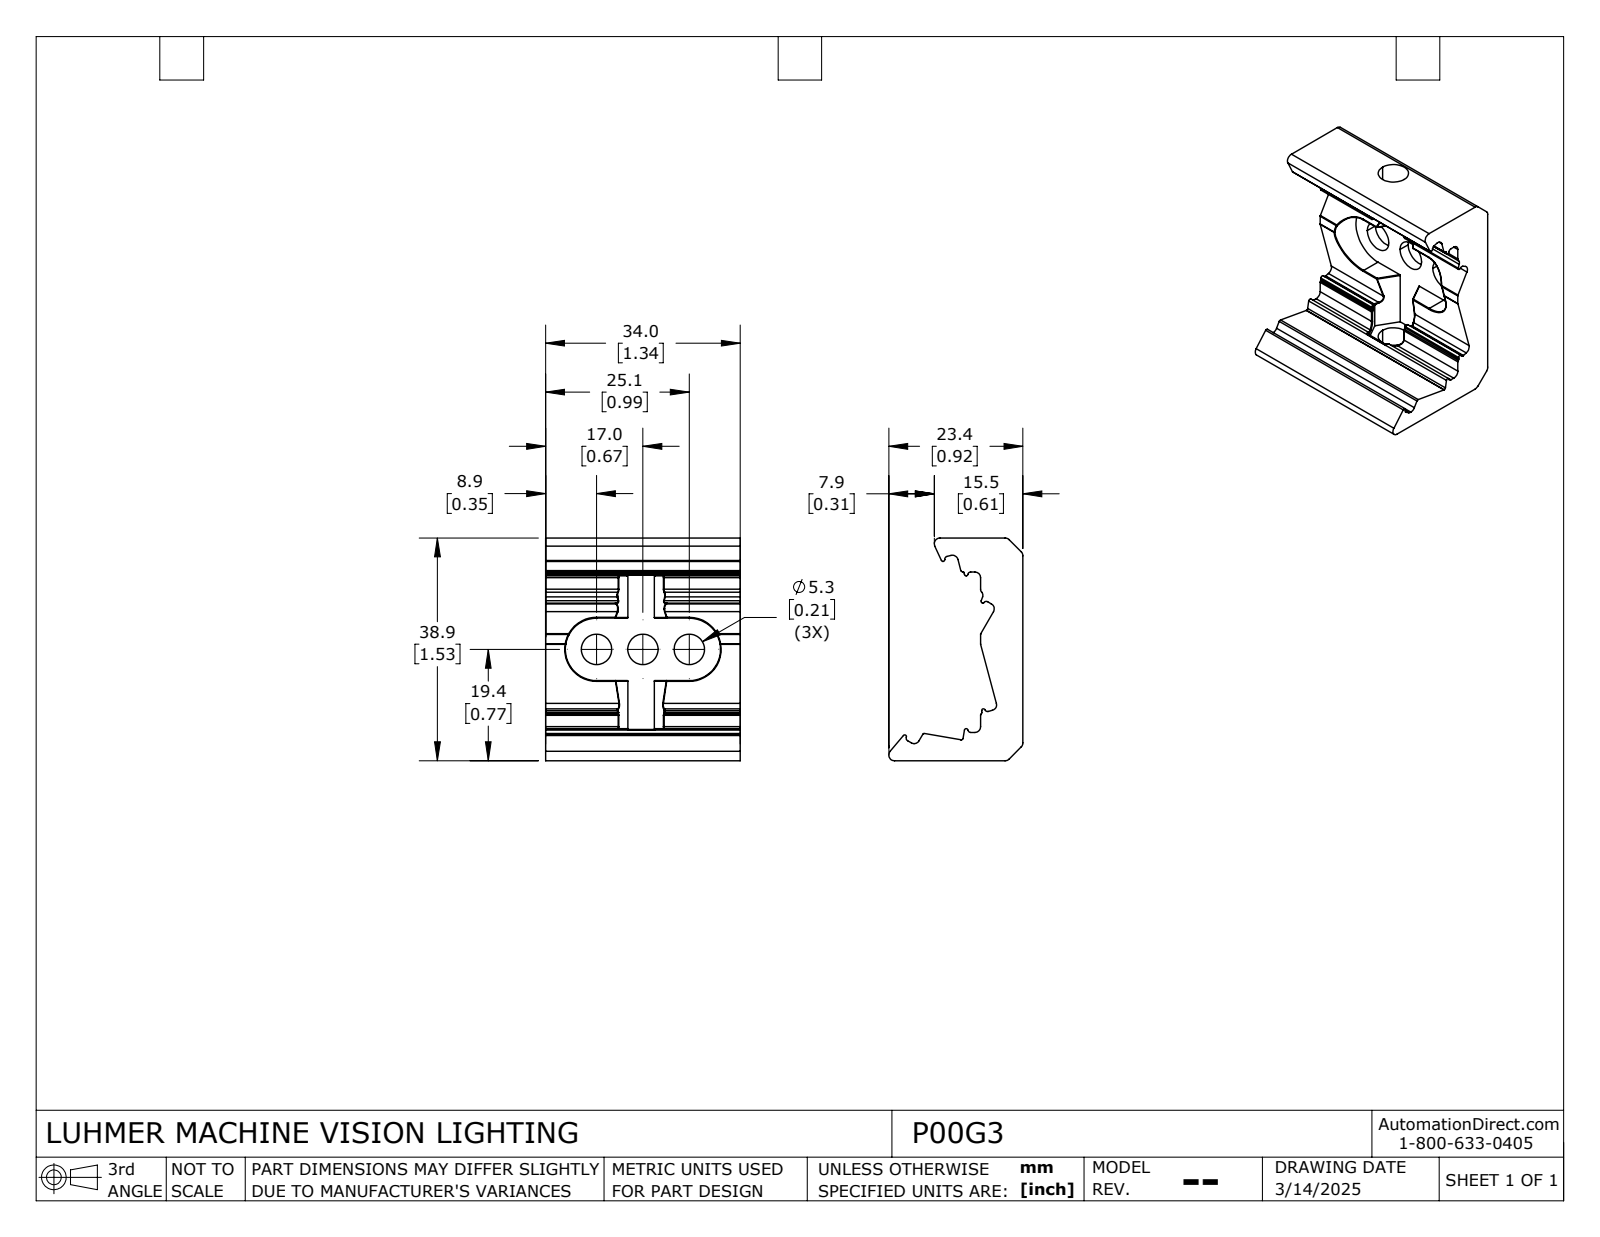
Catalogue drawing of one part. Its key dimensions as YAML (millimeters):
part_name: "P00G3"
step_written_by: "SolidWorks 2024 (AUTOMOTIVE_DESIGN)"
units: millimeters
bodies: {solids: 1, faces: 216, planar: 55, cylindrical: 105, other: 56}
overall_size: [38.9, 34, 23.4]
volume: 9770
surface_area: 6029
round_holes:
  - {diameter: 5.3, count: 4}
partial_cylinders:
  - {radius: 0.1, count: 28}
  - {radius: 0.3, count: 14}
  - {radius: 1, count: 12}
  - {radius: 0.5, count: 6}
  - {radius: 0.8, count: 2}
  - {radius: 5.5, count: 2}
face_to_face_distances: [38.9, 34, 2, 7.4, 5.4, 8, 4, 34.9, 14, 24.9]
hole_center_spacings: [8.1, 16.2]
